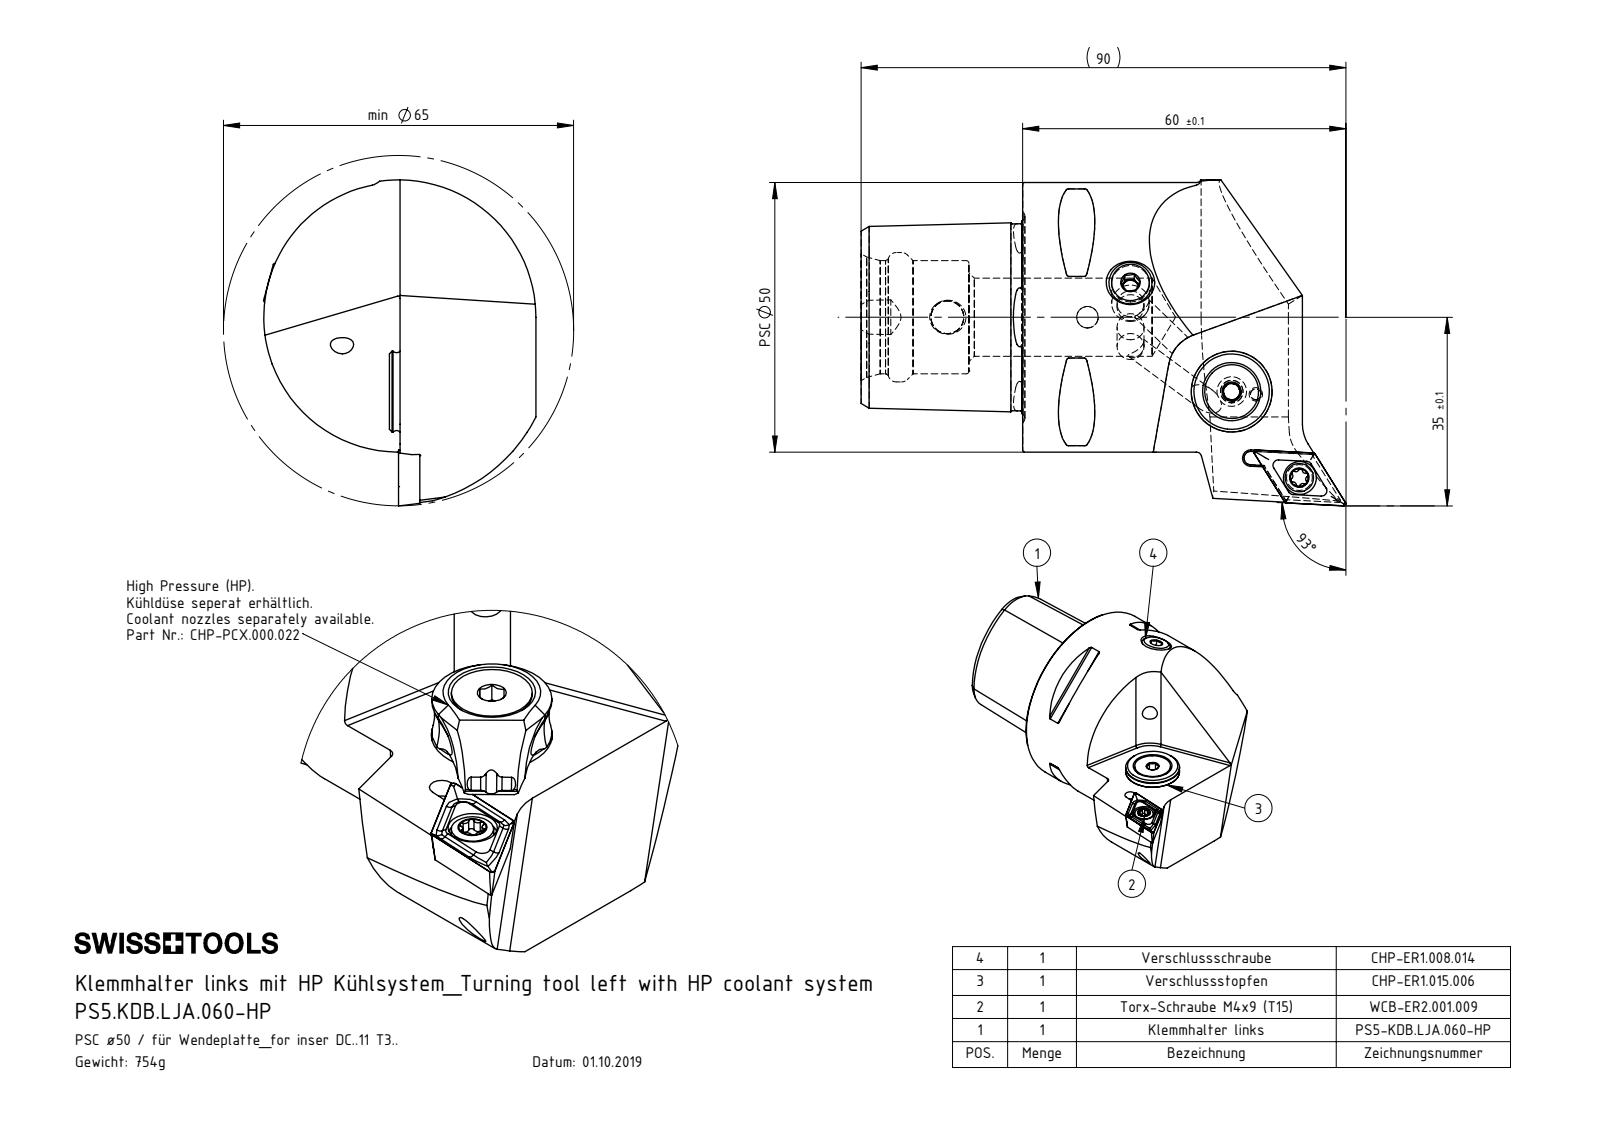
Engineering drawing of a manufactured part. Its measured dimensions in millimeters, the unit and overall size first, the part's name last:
Units: millimetres
Overall size (bounding box): 90.01 × 60.5 × 50.55
Round holes (diameter × count): ⌀4.2 ×3, ⌀6.1 ×2, ⌀1.2 ×1, ⌀2 ×1, ⌀2.5 ×1, ⌀3 ×1, ⌀3.3 ×1, ⌀4 ×1, ⌀4.4 ×1, ⌀5 ×1, ⌀5.2 ×1, ⌀7 ×1
Round bosses / shafts (diameter × count): ⌀50 ×1, ⌀15 ×1, ⌀13.4 ×1, ⌀10 ×1, ⌀8 ×1, ⌀5.5 ×1, ⌀5.25 ×1, ⌀5 ×1
Partial cylindrical surfaces — rounded edges, fillets, slot ends (radius × count): R0.5 ×10, R0.34 ×6, R0.59 ×6, R7 ×2, R1.25 ×1, R4 ×1, R25.5 ×1, R30 ×1
Main face-to-face distances: 30, 25.2, 20.7, 4.5, 19.18, 21.53, 0.83, 3.67, 44.4, 10
Hole centre spacings: 4.5, 17.43, 17.54, 20.3, 20.42, 26, 30.13, 34.38
Volume: 95 695 mm³ · Surface area: 21 954 mm²
Bodies: 8 solids, 271 faces (91 planar, 63 cylindrical, 117 other)
Part name (STEP PRODUCT): ISO 8752 2x8; DCMT11T304; CHP-ER1.015.006; DIN 7991 - M5x15 (+6 more)
STEP written by: SolidWorks 2017 (AUTOMOTIVE_DESIGN)
